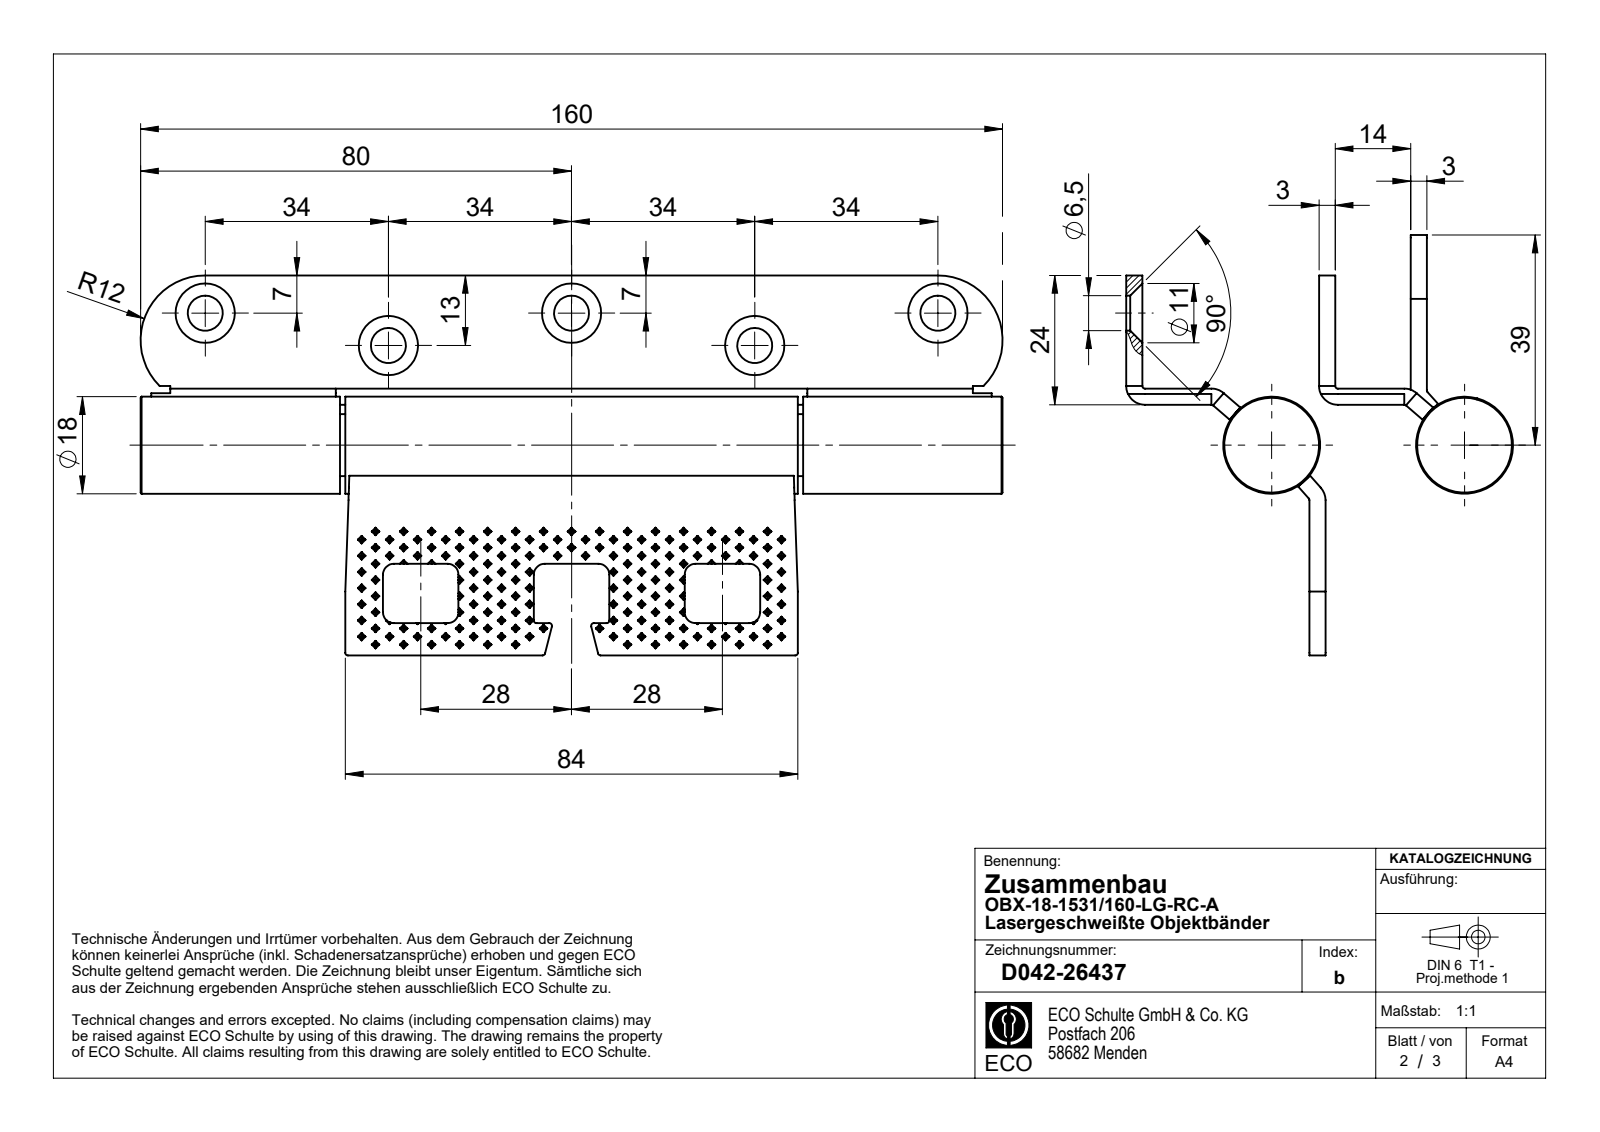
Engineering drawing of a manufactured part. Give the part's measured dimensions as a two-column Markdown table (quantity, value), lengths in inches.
| quantity | value |
| --- | --- |
| part name | D043-14313; OBX-18-1531-160-LG-RC-A_D042-26437; D044-14309; D043-25250 (+4 more) |
| STEP written by | SolidWorks 2020 (CONFIG_CONTROL_DESIGN) |
| units | inches |
| bodies | 11 solids, 1826 faces (1598 planar, 131 cylindrical, 97 other) |
| overall size | 6.299 × 1.89 × 1.417 |
| volume | 3.865 in³ |
| surface area | 54.52 in² |
| round holes (diameter × count) | 0.256 × 5, 0.079 × 2, 0.02 × 1, 0.177 × 1, 0.311 × 1 |
| round bosses / shafts (diameter × count) | 0.709 × 1, 0.472 × 1, 0.465 × 1, 0.453 × 1, 0.303 × 1, 0.157 × 1, 0.065 × 1 |
| partial cylindrical surfaces (radius × count) | 0.02 × 11, 0.079 × 10, 0.01 × 6, 0.138 × 3, 0.027 × 2, 0.083 × 2, 0.118 × 2, 0.472 × 2 |
| main face-to-face distances | 0.118, 0.669, 0.551, 0.787, 4.803, 0.453, 0.827, 0.945, 1.496, 1.004 |
| hole center spacings | 1.359, 2.677, 4.023, 0.077, 0.167, 0.181, 5.354 |
